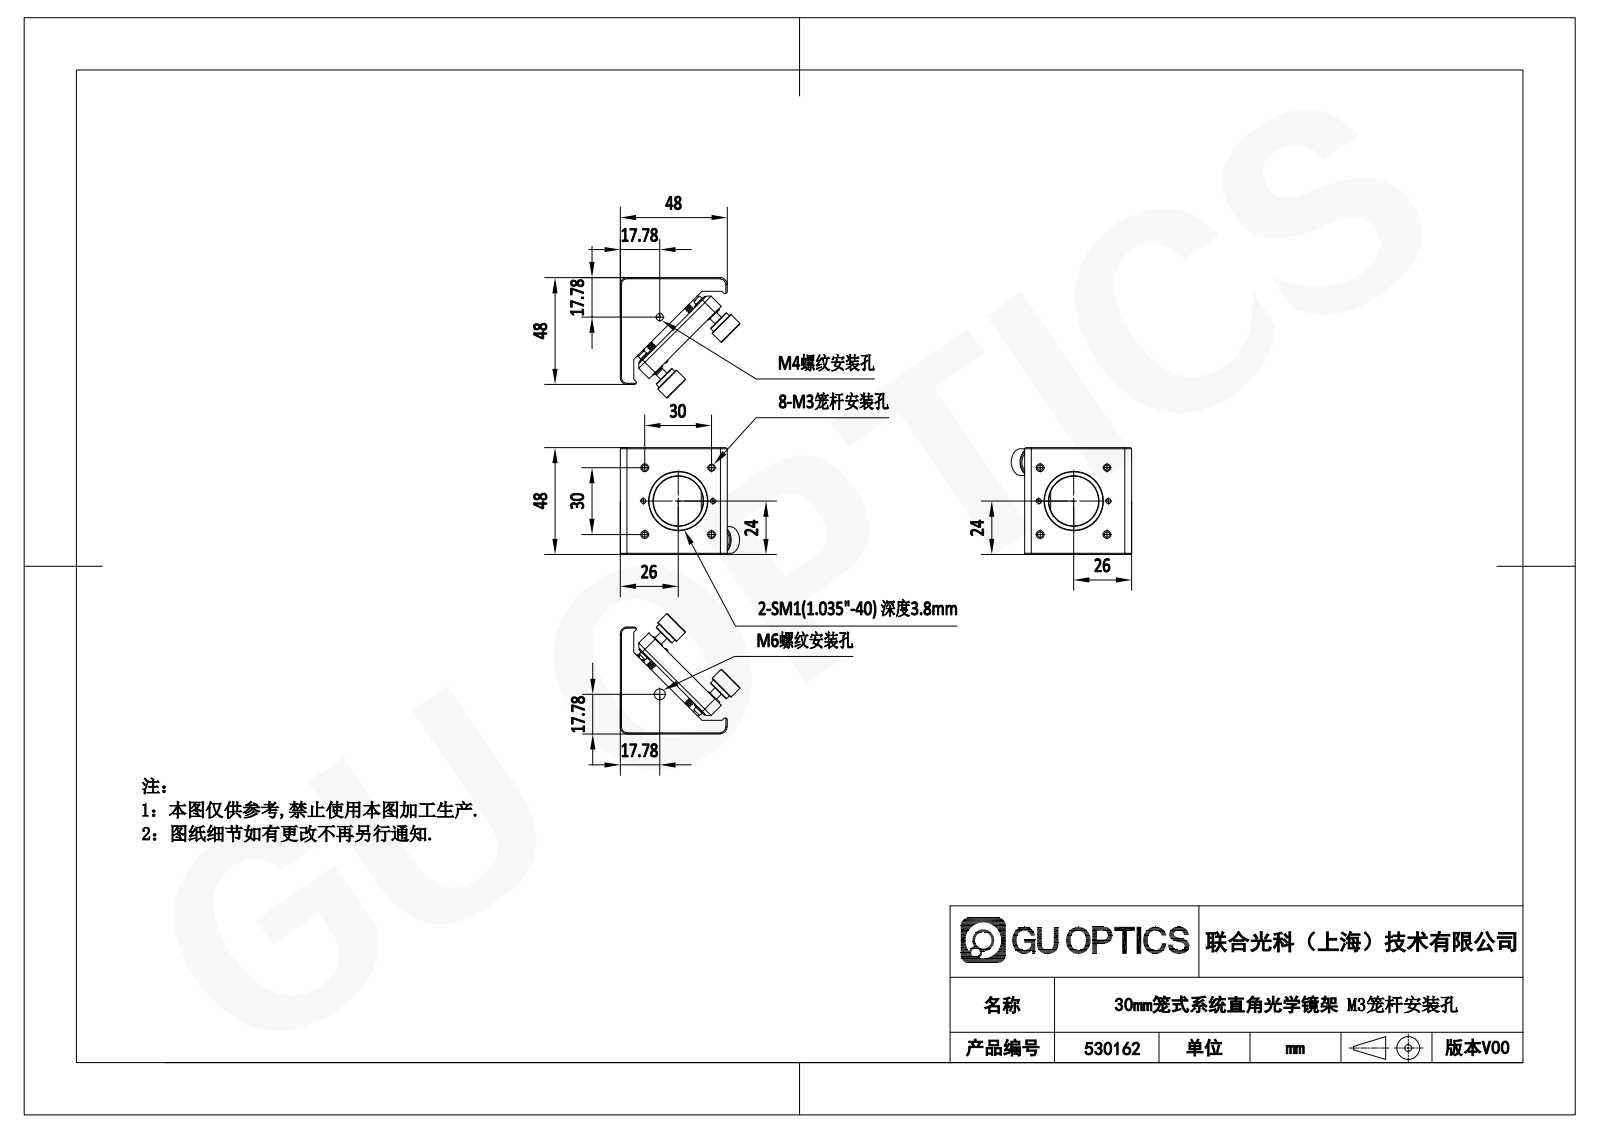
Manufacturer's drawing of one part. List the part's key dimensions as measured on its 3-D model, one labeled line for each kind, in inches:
Part name (STEP PRODUCT): 530162
STEP written by: SolidWorks 2020 (CONFIG_CONTROL_DESIGN)
Units: inches
Bodies: 26 solids, 423 faces (200 planar, 129 cylindrical, 94 other)
Overall size (bounding box): 2.126 × 2.115 × 1.89
Volume: 2.692 in³ · Surface area: 31.64 in²
Round holes (diameter × count): ⌀0.098 ×8, ⌀0.096 ×4, ⌀0.114 ×3, ⌀0.118 ×3, ⌀0.13 ×3, ⌀0.146 ×3, ⌀0.157 ×3, ⌀0.236 ×3, ⌀0.063 ×2, ⌀0.138 ×2, ⌀0.148 ×2, ⌀0.88 ×2
Round bosses / shafts (diameter × count): ⌀0.059 ×4, ⌀0.268 ×3, ⌀0.236 ×3, ⌀0.217 ×3, ⌀0.157 ×3, ⌀0.472 ×2, ⌀0.394 ×2, ⌀0.197 ×1
Partial cylindrical surfaces — rounded edges, fillets, slot ends (radius × count): R0.059 ×14, R0.039 ×12, R0.03 ×6, R0.031 ×4, R0.157 ×4, R0.197 ×4, R0.118 ×3, R0.144 ×3
Main face-to-face distances: 1.89, 0.241, 0.433, 0.315, 0.118, 0.039, 1.85, 0.15, 0.091, 1.74
Hole centre spacings: 0.591, 0.835, 1.181, 1.343, 0.615, 1.101, 1.378, 1.67
